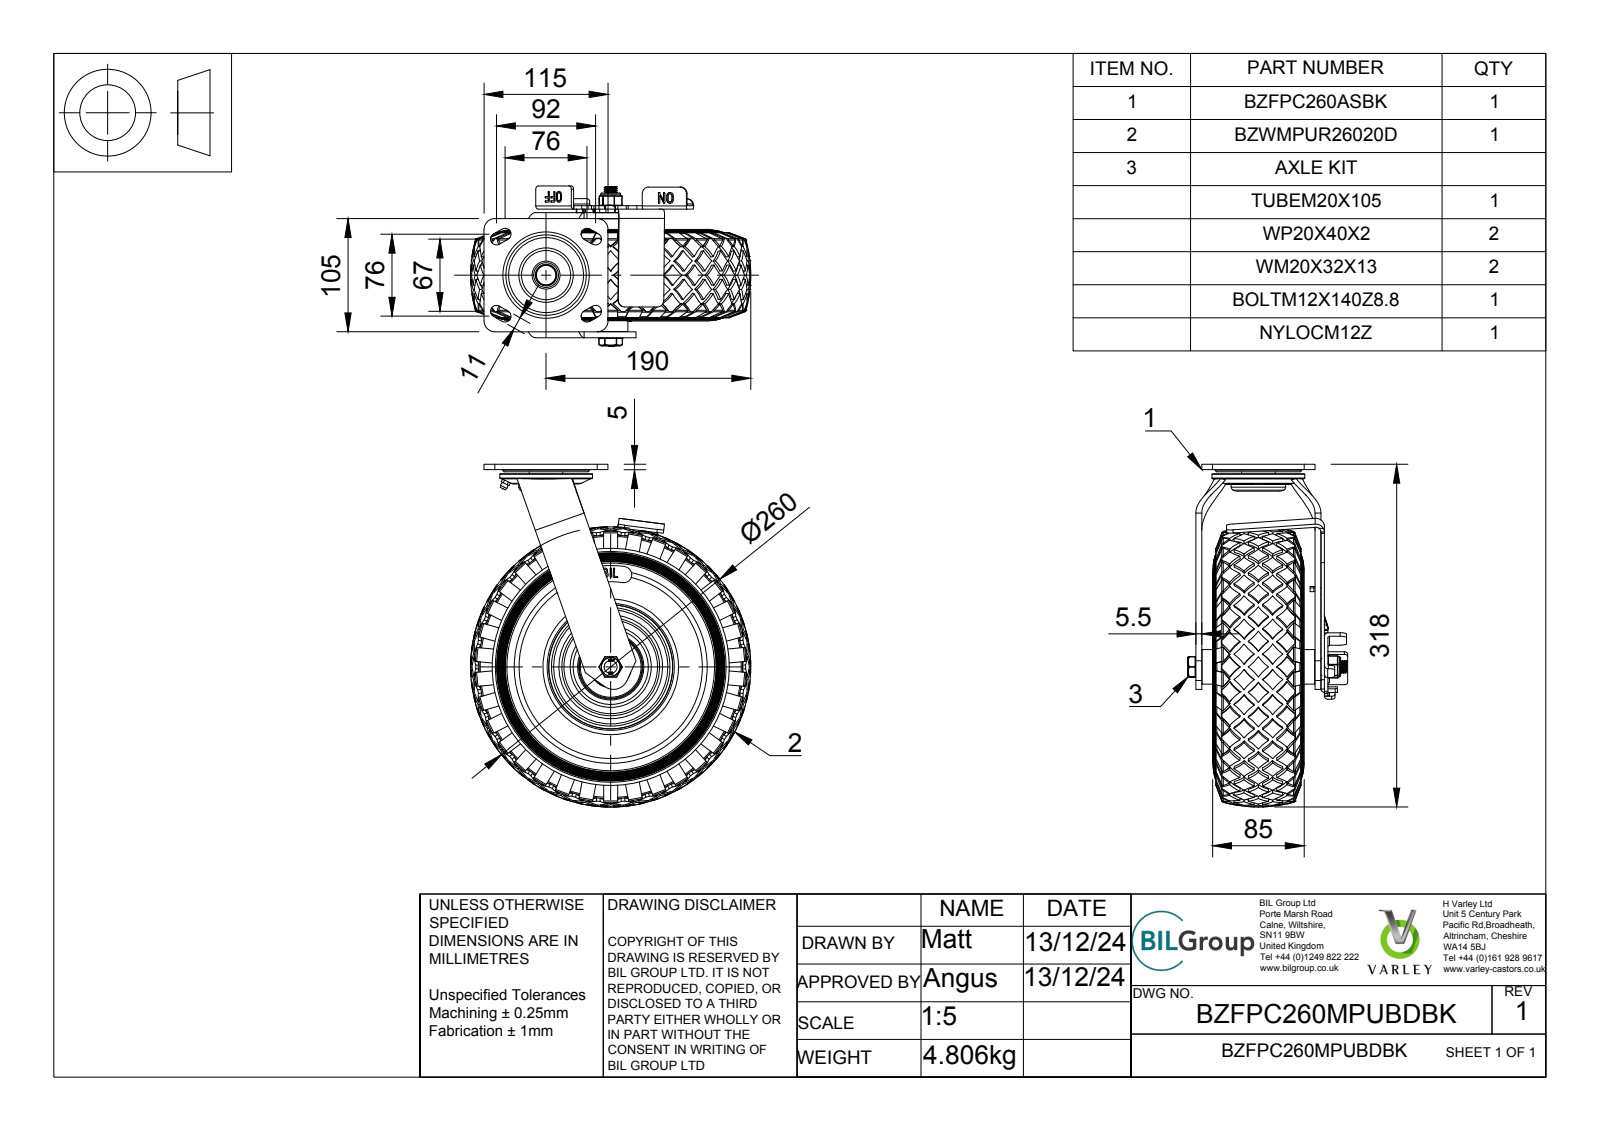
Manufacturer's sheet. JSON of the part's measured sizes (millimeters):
{"part_name": "BZFPC260MPUBDBK v5; BZFPC260ASBK v1; FABRICATED STEEL TOP PLATE; FABRICATED STEEL FORKS (+8 more)", "step_written_by": "Autodesk Translation Framework v13.20.0.188 (AP242_MANAGED_MODEL_BASED_3D_ENGINEERING_MIM_LF)", "units": "millimeters", "bodies": {"solids": 28, "faces": 2441, "planar": 738, "cylindrical": 377, "other": 1326}, "overall_size": [317.97, 259.97, 148.5], "volume_mm3": 3772000, "surface_area_mm2": 463346, "round_holes": [[9, 1], [12, 1], [12.5, 1], [13, 1], [13.8, 1], [14, 1], [16.2, 1], [20, 1], [21, 1], [22, 1], [29.8, 1], [35, 1]], "round_bosses_or_shafts": [[7.5, 8], [220, 1], [86, 1], [80, 1], [61.5, 1], [58, 1], [50.5, 1], [37.5, 1]], "partial_cylinders_radius": [[2, 71], [120.85, 34], [0.5, 24], [3, 11], [5.5, 8], [6, 8], [0.1, 6], [10, 5]], "face_to_face_distances": [3.25, 110.5, 5.5, 3, 12, 92, 18.5, 113.75, 8.75, 105], "hole_center_spacings": [41.77]}
